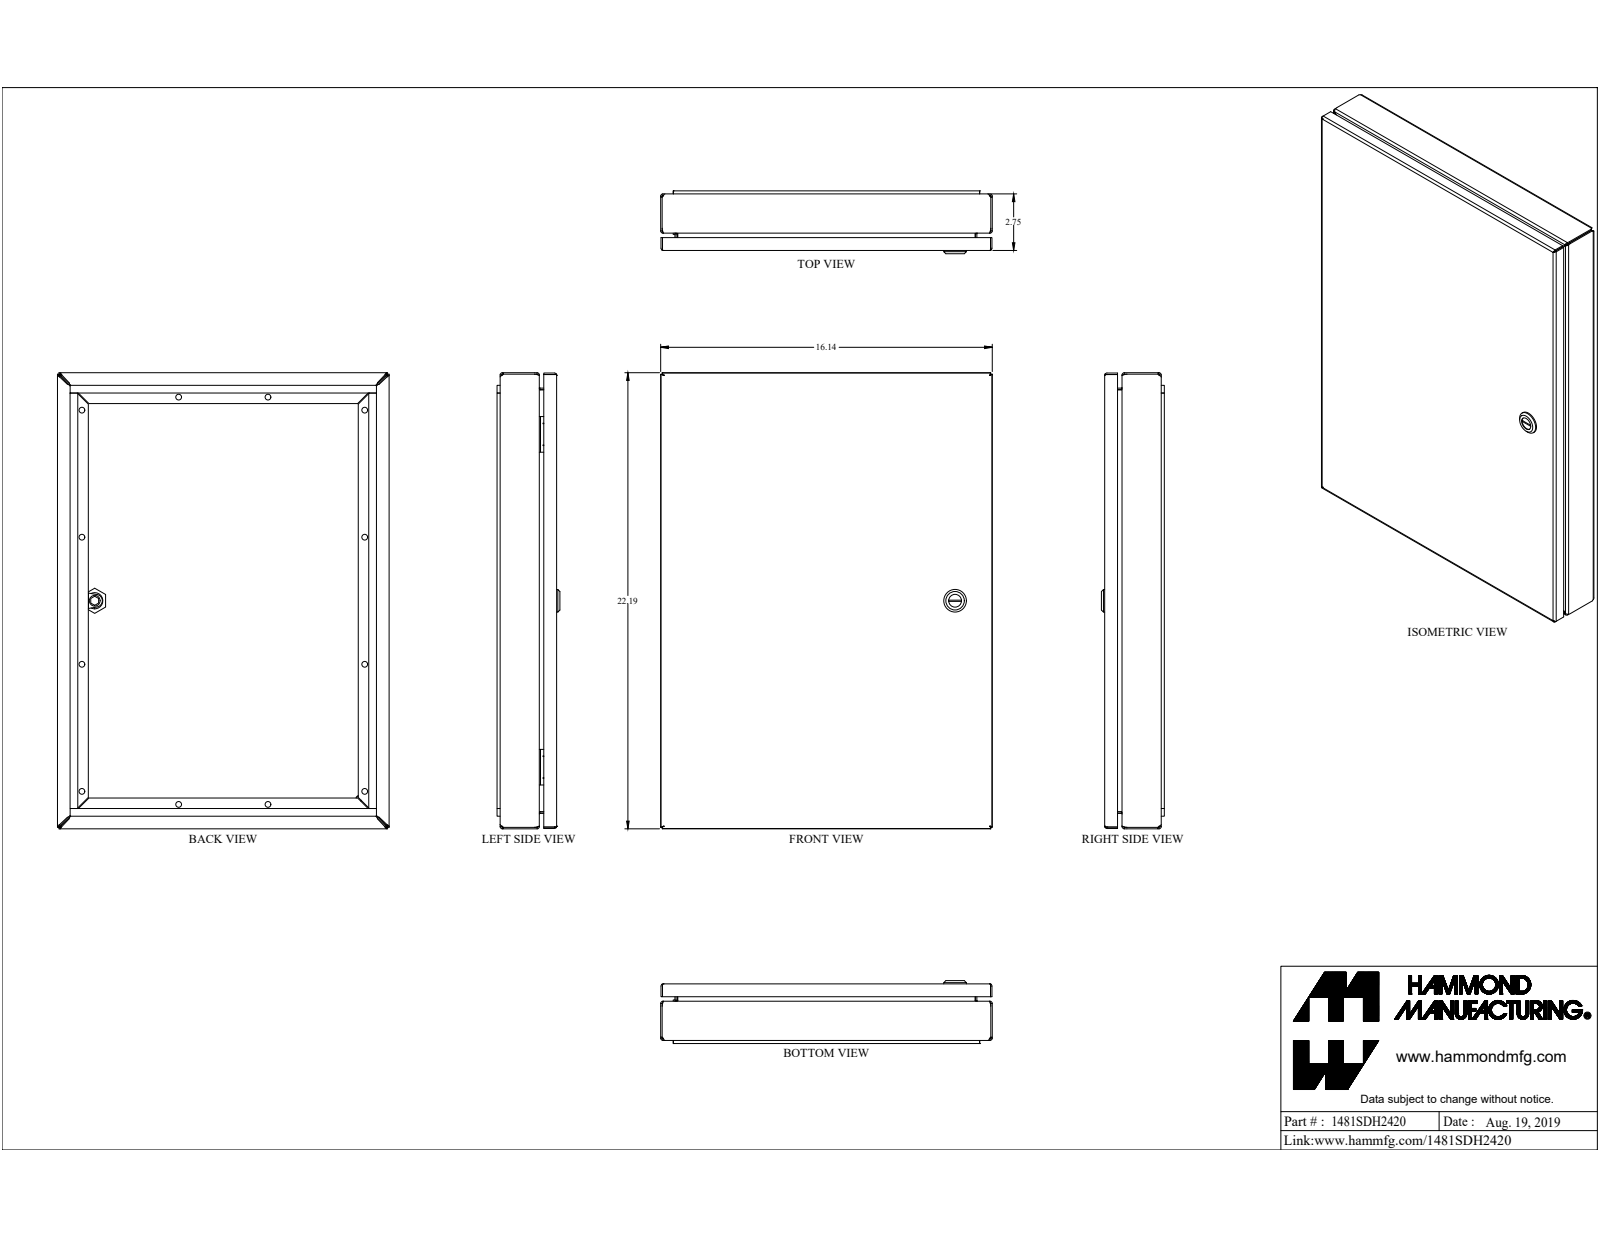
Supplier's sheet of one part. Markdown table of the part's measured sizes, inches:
| quantity | value |
| --- | --- |
| part name | 1481SDH2420 |
| STEP written by | SolidWorks 2019 (CONFIG_CONTROL_DESIGN) |
| units | inches |
| bodies | 23 solids, 618 faces (348 planar, 172 cylindrical, 98 other) |
| overall size | 22.19 × 16.14 × 3.061 |
| volume | 67.97 in³ |
| surface area | 1 776 in² |
| round holes (diameter × count) | 0.281 × 12, 0.172 × 1, 0.232 × 1, 0.24 × 1, 0.242 × 1, 0.625 × 1, 0.785 × 1 |
| round bosses / shafts (diameter × count) | 1.1 × 1, 0.525 × 1, 0.455 × 1, 0.398 × 1, 0.356 × 1, 0.313 × 1, 0.292 × 1, 0.25 × 1 |
| partial cylindrical surfaces (radius × count) | 0.036 × 28, 0.108 × 28, 0.382 × 12, 19.003 × 8, 0.006 × 4, 0.062 × 4, 0.25 × 4, 0.499 × 4 |
| main face-to-face distances | 0.072, 2.579, 0.843, 1.736, 2.651, 16.068, 2.507, 2.679, 1.836, 0.1 |
| hole center spacings | 4.75, 6.182, 9.078, 11.335, 13.764, 15.088, 15.842, 18.502 |
